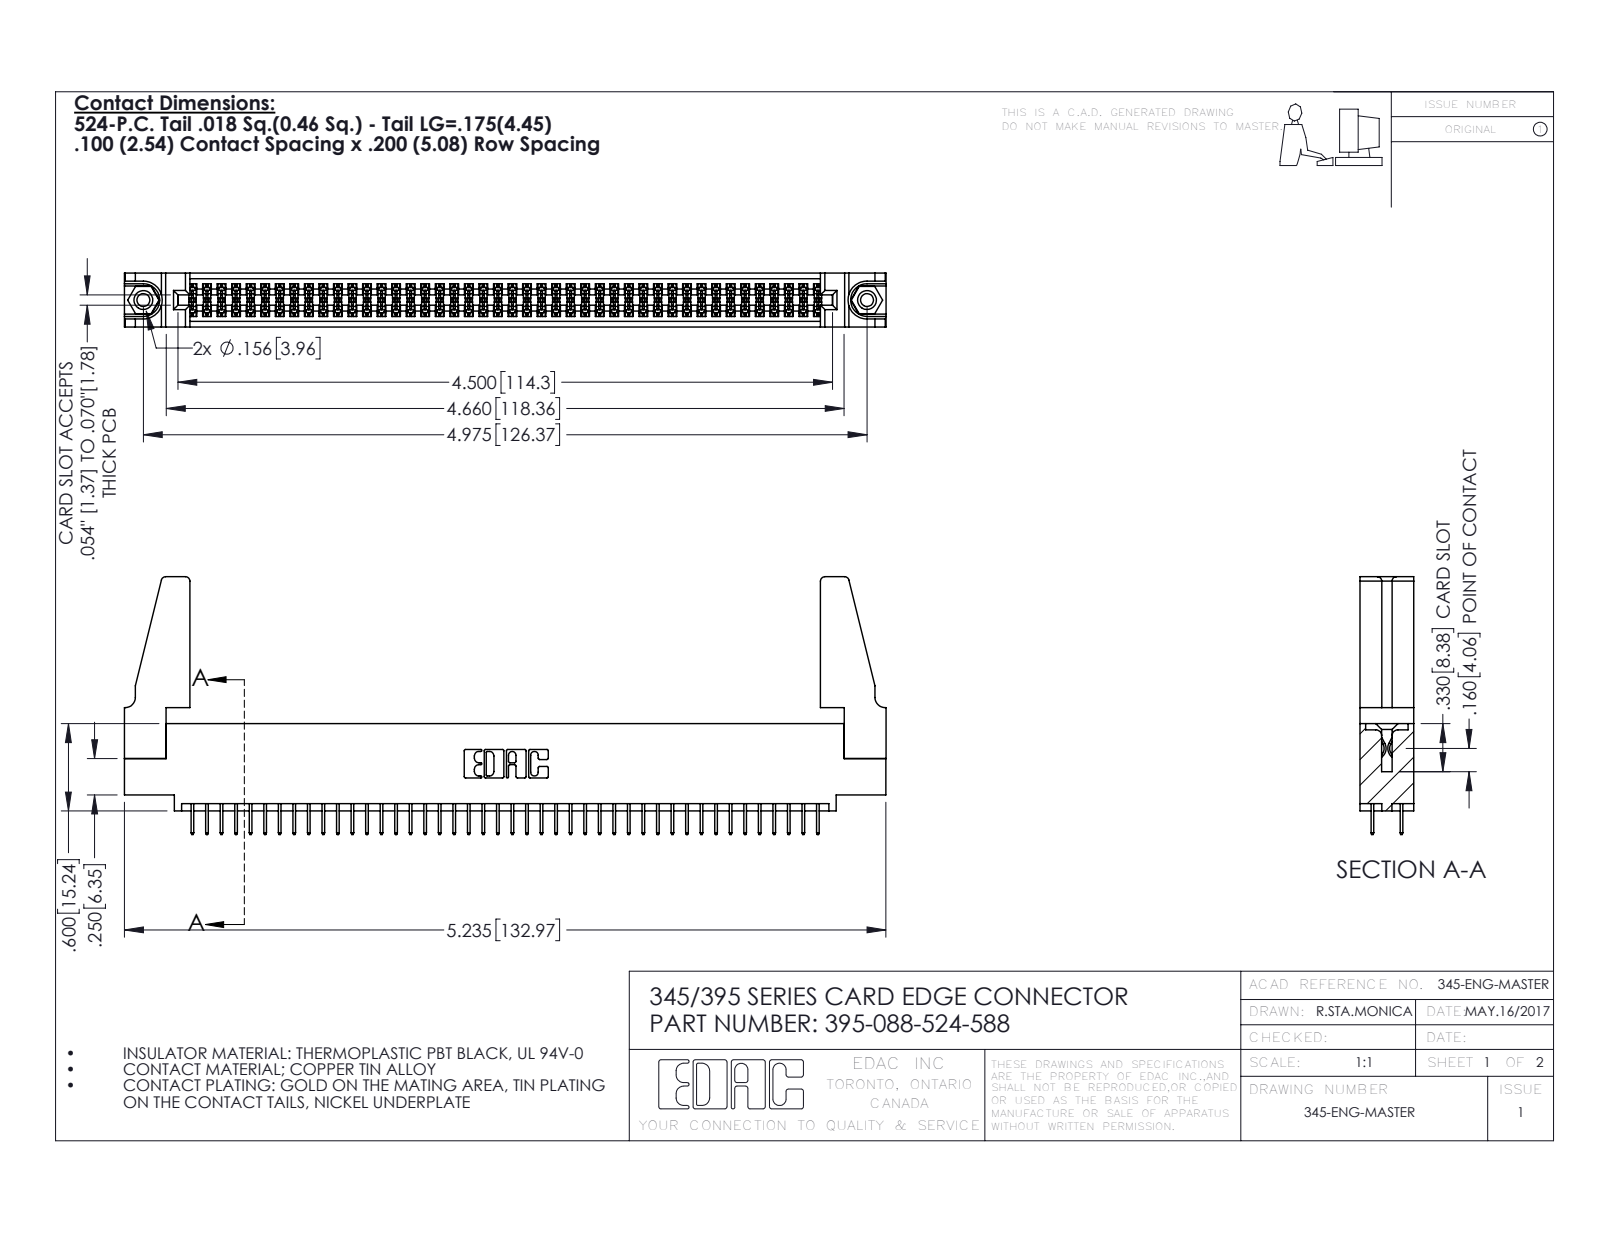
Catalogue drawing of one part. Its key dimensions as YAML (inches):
part_name: "345-250-001_345-250-001-102; 395-088-524-588; 345-220-078_345-220-088; 345 Part_0.110 Offset - 0.156 Dia-TH (+1 more)"
step_written_by: "SolidWorks 2016 (CONFIG_CONTROL_DESIGN)"
units: inches
bodies: {solids: 93, faces: 5006, planar: 3588, cylindrical: 1402, other: 16}
overall_size: [5.236, 1.772, 0.37]
volume: 0.975
surface_area: 33.67
round_holes:
  - {diameter: 0.089, count: 2}
  - {diameter: 0.125, count: 2}
  - {diameter: 0.156, count: 2}
  - {diameter: 0.064, count: 1}
round_bosses_or_shafts:
  - {diameter: 0.155, count: 2}
partial_cylinders:
  - {radius: 0.006, count: 132}
  - {radius: 0.01, count: 22}
  - {radius: 0.03, count: 8}
  - {radius: 0.007, count: 6}
  - {radius: 0.031, count: 6}
  - {radius: 0.026, count: 3}
  - {radius: 0.014, count: 2}
  - {radius: 0.019, count: 2}
face_to_face_distances: [0.072, 0.298, 0.37, 0.2, 0.098, 0.272, 0.025, 0.225, 0.072, 0.175]
hole_center_spacings: [0.27, 4.739, 4.975]
